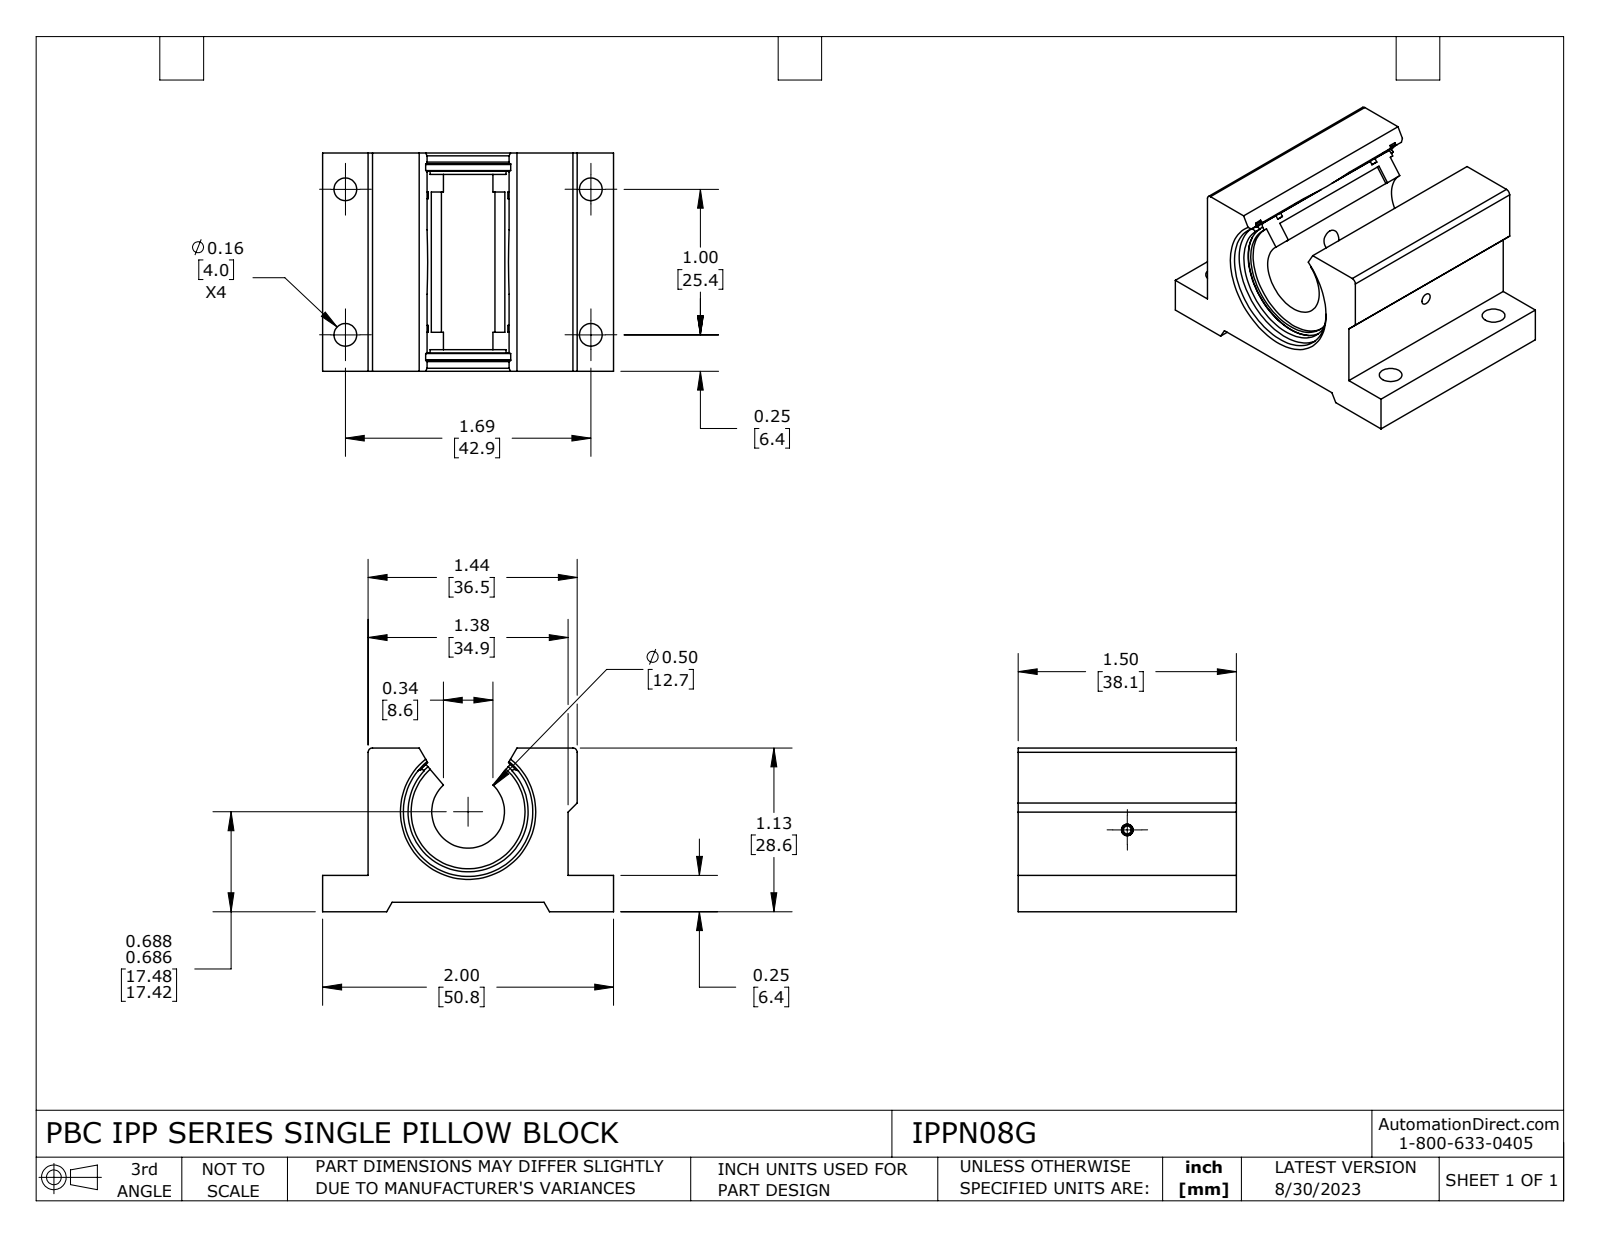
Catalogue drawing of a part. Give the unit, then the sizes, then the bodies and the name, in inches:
Units: inches
Overall size (bounding box): 2 × 1.5 × 1.125
Round holes (diameter × count): ⌀0.156 ×4, ⌀0.054 ×1, ⌀0.079 ×1, ⌀0.136 ×1
Round bosses / shafts (diameter × count): ⌀0.078 ×1
Partial cylindrical surfaces — rounded edges, fillets, slot ends (radius × count): R0.03 ×4, R0.12 ×2, R0.25 ×1, R0.378 ×1, R0.392 ×1, R0.41 ×1, R0.413 ×1, R0.438 ×1
Main face-to-face distances: 0.065, 0.25, 1.125, 1.06, 1.5, 0.185, 0.875, 0.313, 1.687, 1.375
Hole centre spacings: 1, 1.687, 1.961
Volume: 1.879 in³ · Surface area: 21.15 in²
Bodies: 5 solids, 152 faces (47 planar, 74 cylindrical, 31 other)
Part name (STEP PRODUCT): IPPN08G
STEP written by: SolidWorks 2021 (CONFIG_CONTROL_DESIGN)
